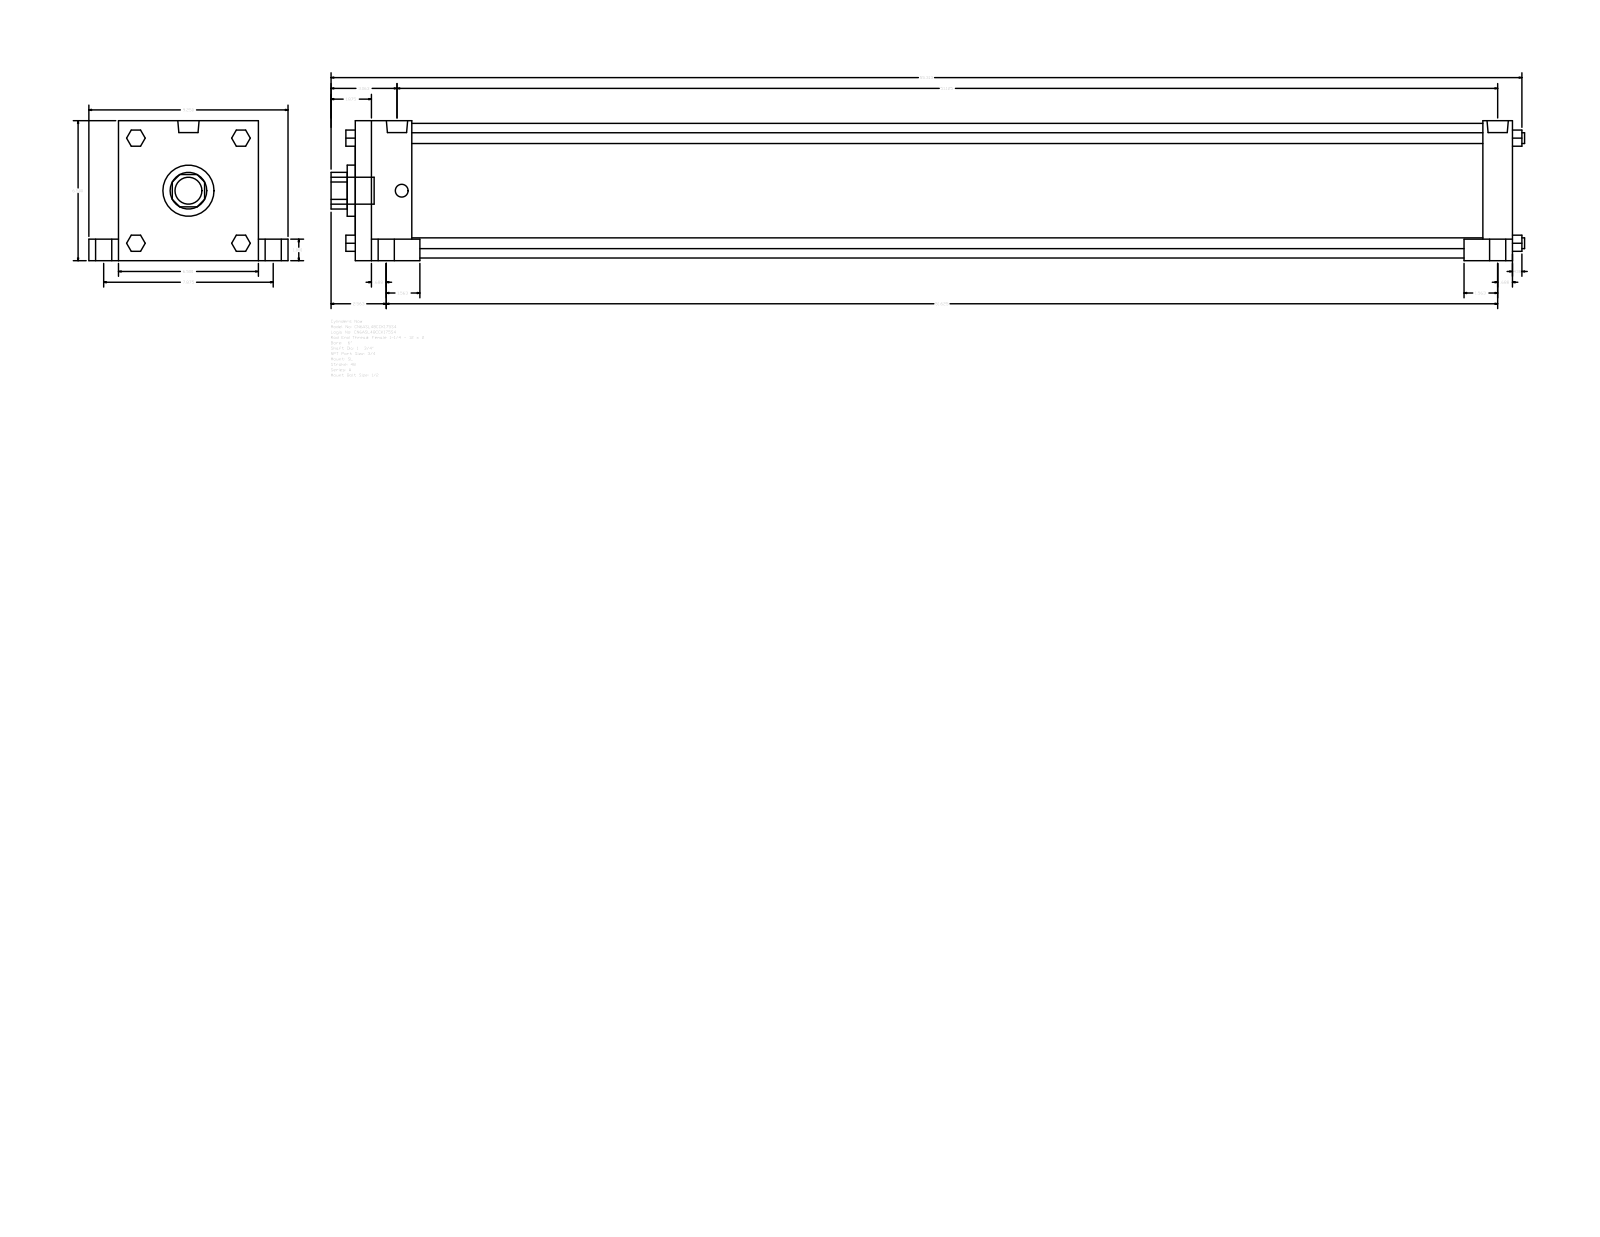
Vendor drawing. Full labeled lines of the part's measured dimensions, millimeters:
Part name (STEP PRODUCT): A_SL__0600_1.75
STEP written by: GSSL Pune (CONFIG_CONTROL_DESIGN)
Units: millimetres
Bodies: 0 solids, 150 faces (114 planar, 36 cylindrical, 0 other)
Overall size (bounding box): 1408.11 × 234.95 × 165.1
Round holes (diameter × count): ⌀44.45 ×1, ⌀60.33 ×1, ⌀158.75 ×1
Round bosses / shafts (diameter × count): ⌀25.4 ×4, ⌀19.05 ×4, ⌀15.08 ×4, ⌀12.7 ×4, ⌀25.12 ×2, ⌀31.75 ×1
Partial cylindrical surfaces — rounded edges, fillets, slot ends (radius × count): R21.63 ×1
Main face-to-face distances: 165.1, 1365.26, 66.68, 1298.58, 1330.33, 1263.65, 34.93, 34.92, 25.4, 139.7
